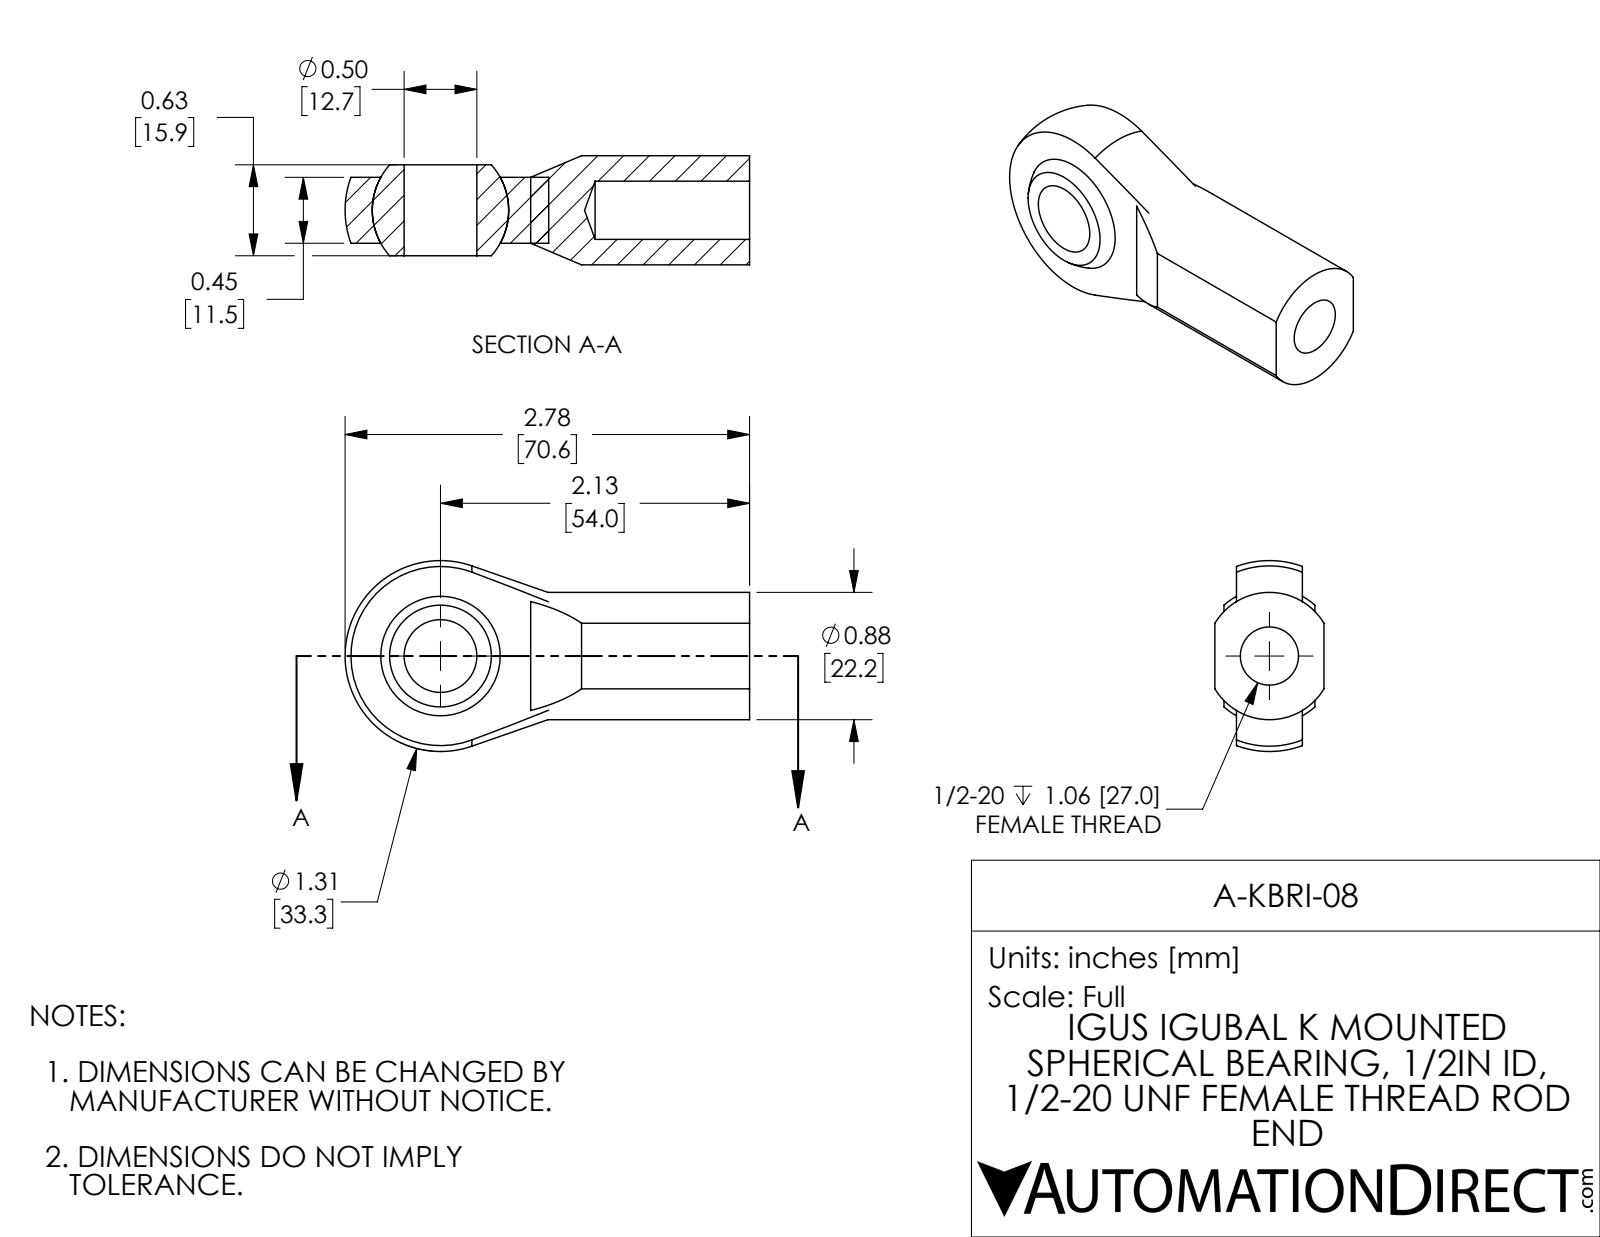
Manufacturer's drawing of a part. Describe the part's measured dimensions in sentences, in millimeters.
The part is named "A-KBRI-08". Its 3-D file was written by "SolidWorks 2017 (AUTOMOTIVE_DESIGN)". It is 3 solids with 30 faces: 11 planar, 7 cylindrical and 12 other. Overall it measures 70.6 by 33.3 by 19.1 millimeters. Its volume is 21 290 cubic millimeters and its surface area 9 406 square millimeters. Round holes: 1 of diameter 10.2, 1 of diameter 12.7. Partial cylindrical surfaces (rounded edges, fillets, slot ends): 1 of radius 11.1. The main face-to-face distances are 3.8, 15.3, 11.5, 19.1, 38.2, 35.1, 3.1, 1.6, 17.5, 2.2.
